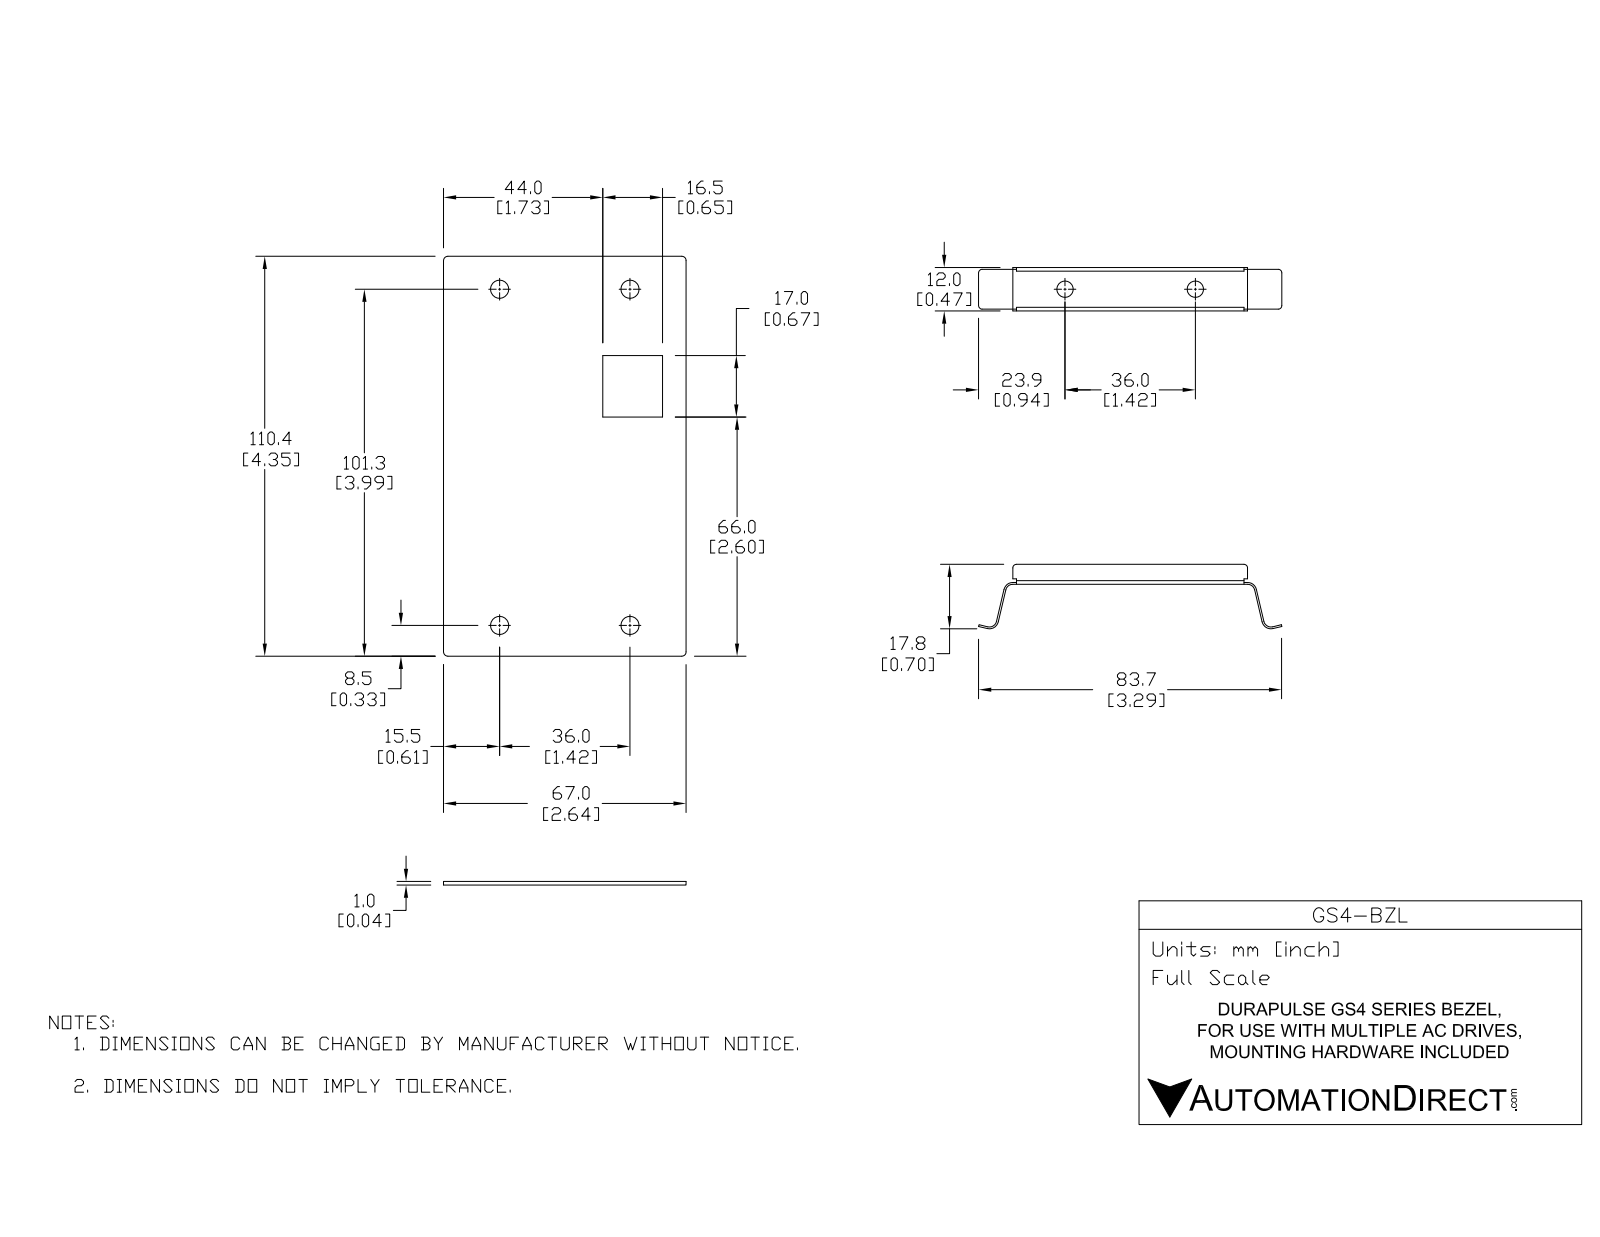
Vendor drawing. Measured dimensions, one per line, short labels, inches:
name: GS4-BZLl
written by: SolidWorks 2015 (AUTOMOTIVE_DESIGN)
unit: in
bodies: 2 solids, 84 faces (44 planar, 36 cylindrical, 4 other)
size: 6.068 × 4.346 × 0.701
volume: 0.483 in³; area: 28.23 in²
holes: 4× ⌀0.197, 2× ⌀0.177
rounds: 6× R0.05, 4× R0.047, 4× R0.079, 4× R0.098, 2× R0.014, 2× R0.025
face distances: 0.039, 0.02, 0.137, 0.098, 0.117, 0.157, 0.453, 0.433, 0.472, 2.638
hole spacings: 1.417, 3.16, 3.654, 3.919, 4.344, 1.791, 3.477, 4.559
